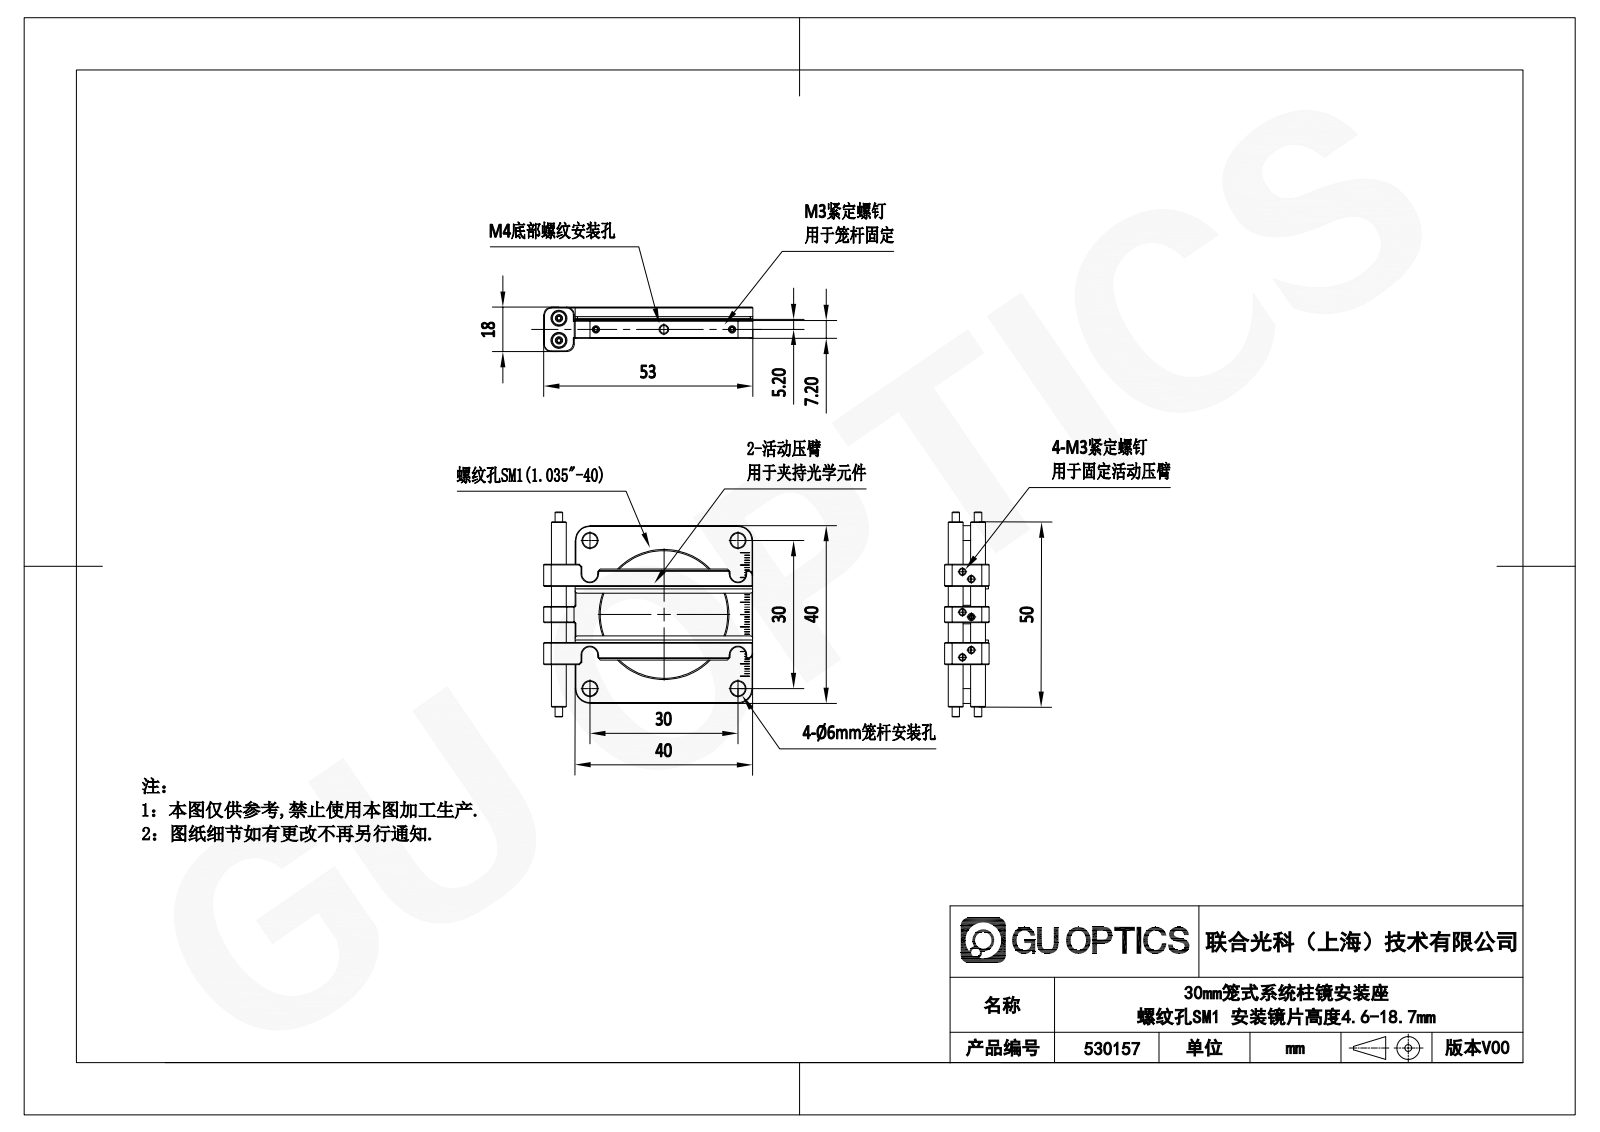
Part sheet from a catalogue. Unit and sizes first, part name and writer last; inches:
Units: inches
Overall size (bounding box): 2.165 × 2.087 × 0.709
Round holes (diameter × count): ⌀0.098 ×10, ⌀0.236 ×6, ⌀0.13 ×1, ⌀1.035 ×1
Round bosses / shafts (diameter × count): ⌀0.118 ×5
Partial cylindrical surfaces — rounded edges, fillets, slot ends (radius × count): R0.039 ×7, R0.118 ×4, R0.128 ×4, R0.197 ×4, R0.016 ×2
Main face-to-face distances: 0.283, 0.299, 0.213, 0.496, 0.016, 0.197, 0.039, 0.562, 0.411, 0.26
Hole centre spacings: 0.835, 1.181, 0.162, 0.411, 0.434, 0.492, 0.589, 0.834
Volume: 0.909 in³ · Surface area: 19.43 in²
Bodies: 16 solids, 682 faces (457 planar, 65 cylindrical, 160 other)
Part name (STEP PRODUCT): 530157
STEP written by: SolidWorks 2020 (CONFIG_CONTROL_DESIGN)
